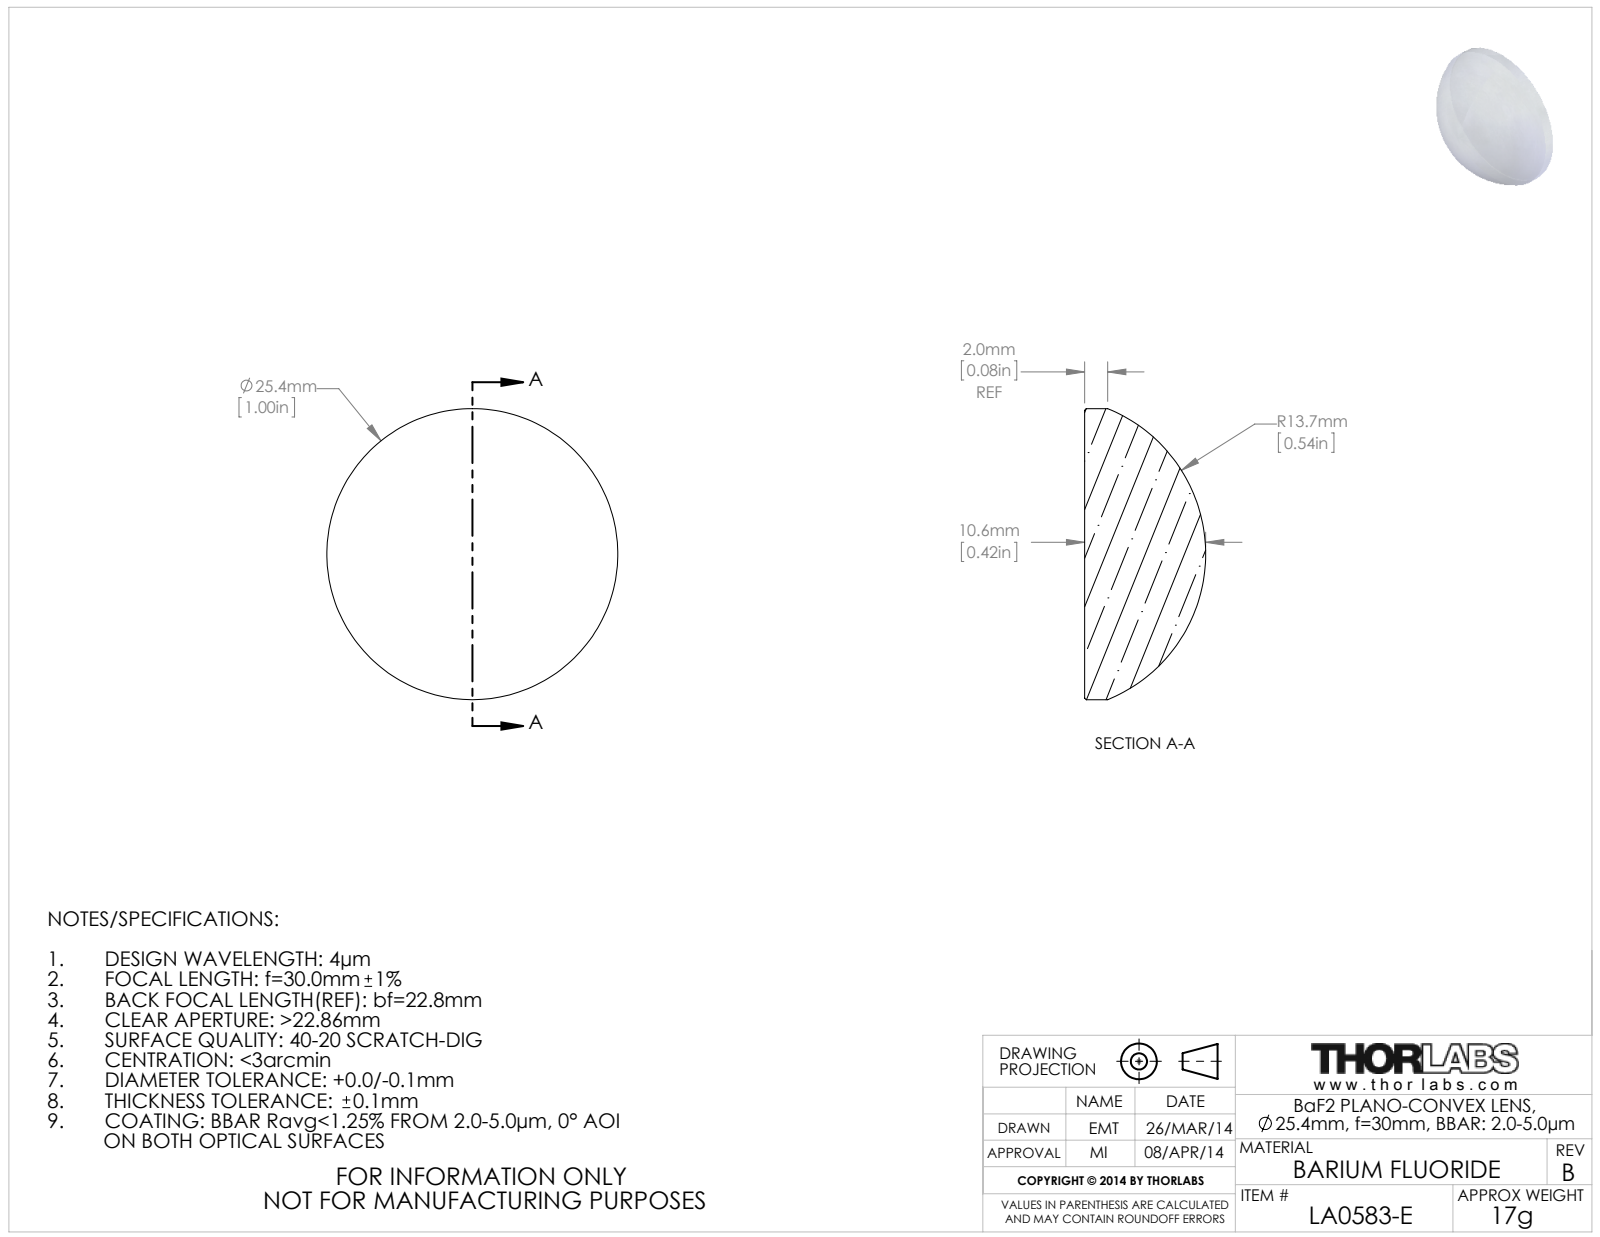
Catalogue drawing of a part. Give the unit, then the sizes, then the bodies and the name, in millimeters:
Units: millimetres
Overall size (bounding box): 25.4 × 25.4 × 10.56
Round bosses / shafts (diameter × count): ⌀25.4 ×1
Volume: 3 510 mm³ · Surface area: 1 397 mm²
Bodies: 1 solid, 7 faces (1 planar, 2 cylindrical, 4 other)
Part name (STEP PRODUCT): 20092-E0W
STEP written by: SolidWorks 2014 (CONFIG_CONTROL_DESIGN)
